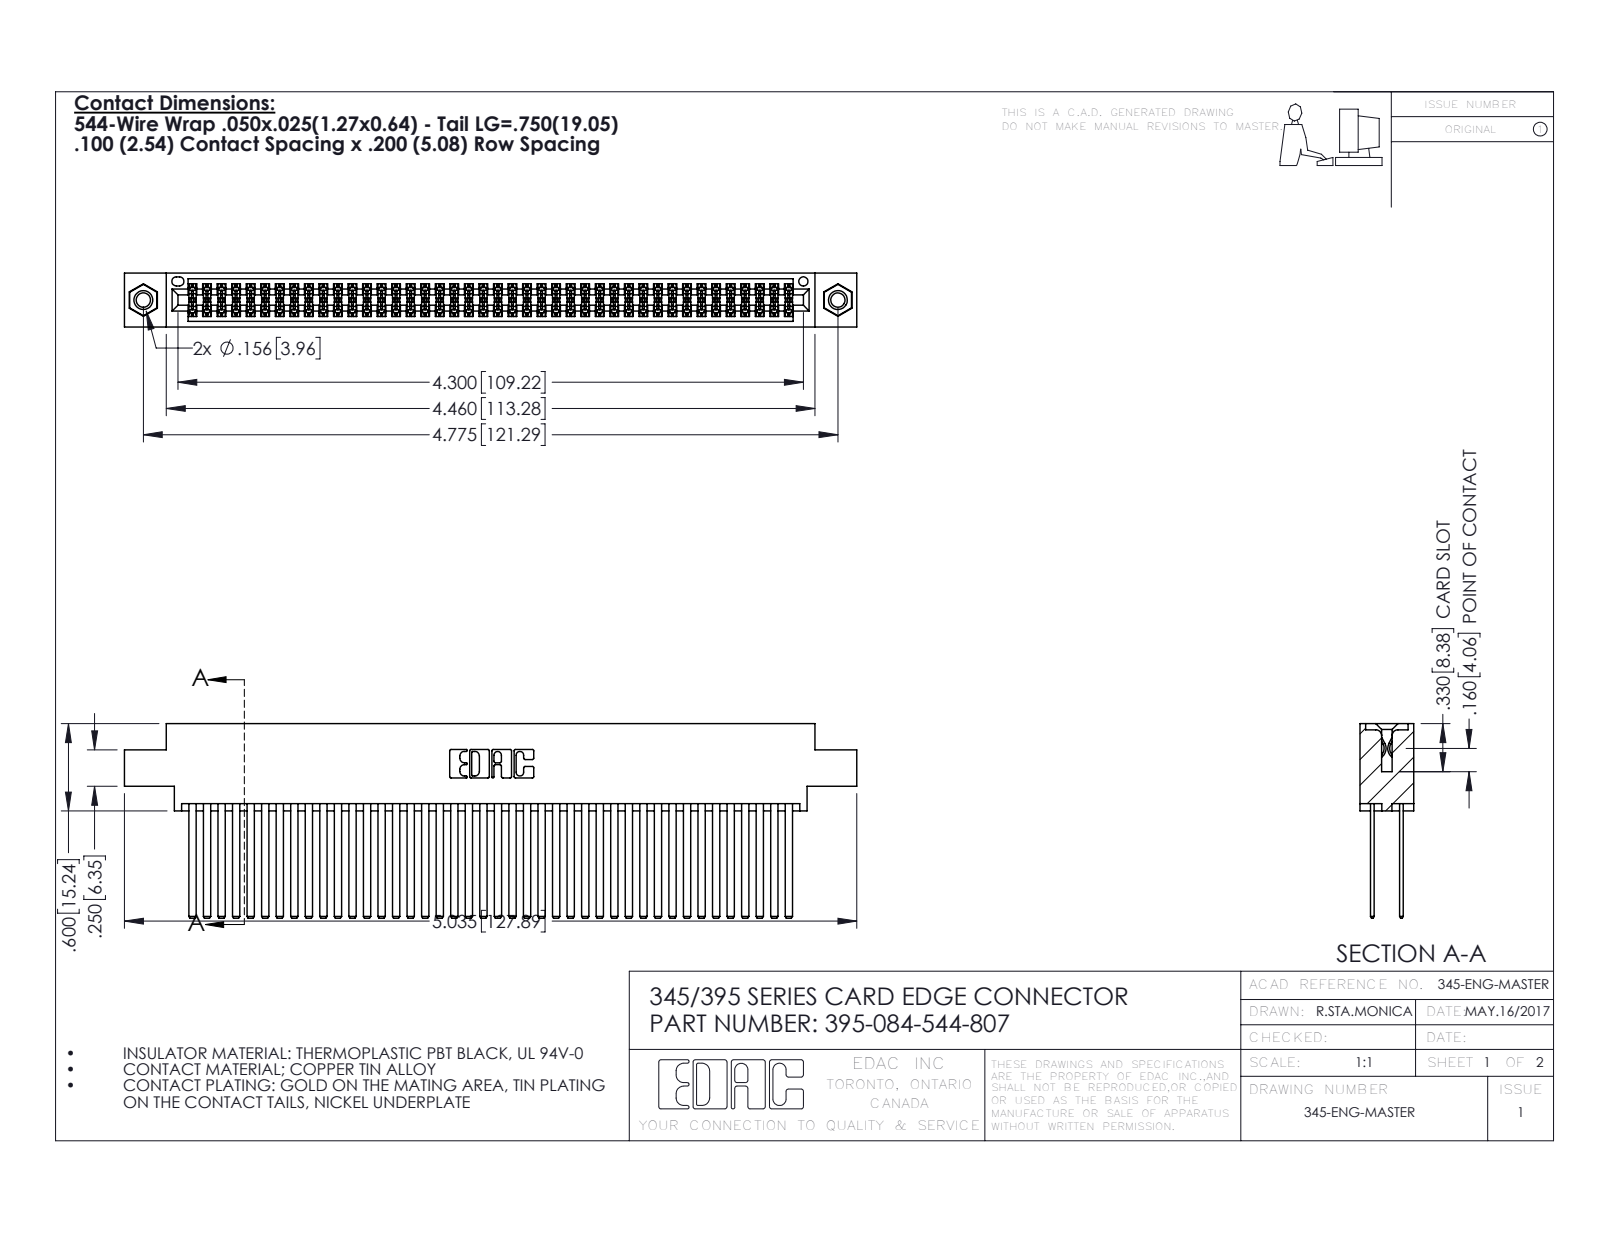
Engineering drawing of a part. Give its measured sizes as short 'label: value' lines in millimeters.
name: 345-292-001_345-293-144; 345-250-001_345-250-005-103; 345 Part_0.170 Offset - 0.156 Dia-TI; 395-084-544-807
written by: SolidWorks 2016 (CONFIG_CONTROL_DESIGN)
unit: mm
bodies: 87 solids, 3886 faces (2552 planar, 1318 cylindrical, 16 other)
size: 127.9 × 34 × 9.4
volume: 13 500 mm³; area: 23 540 mm²
holes: 2× ⌀2.5, 2× ⌀3.2, 2× ⌀4, 1× ⌀1.6
bosses: 2× ⌀3.9
rounds: 126× R0.2, 22× R0.3, 6× R0.2, 6× R0.8, 3× R0.7, 2× R0.4, 2× R0.5, 2× R0.6
face distances: 5.1, 0.6, 1.8, 2.5, 6.9, 7.6, 5.7, 4.4, 9.4, 3.8
hole spacings: 6.9, 115.3, 121.3
